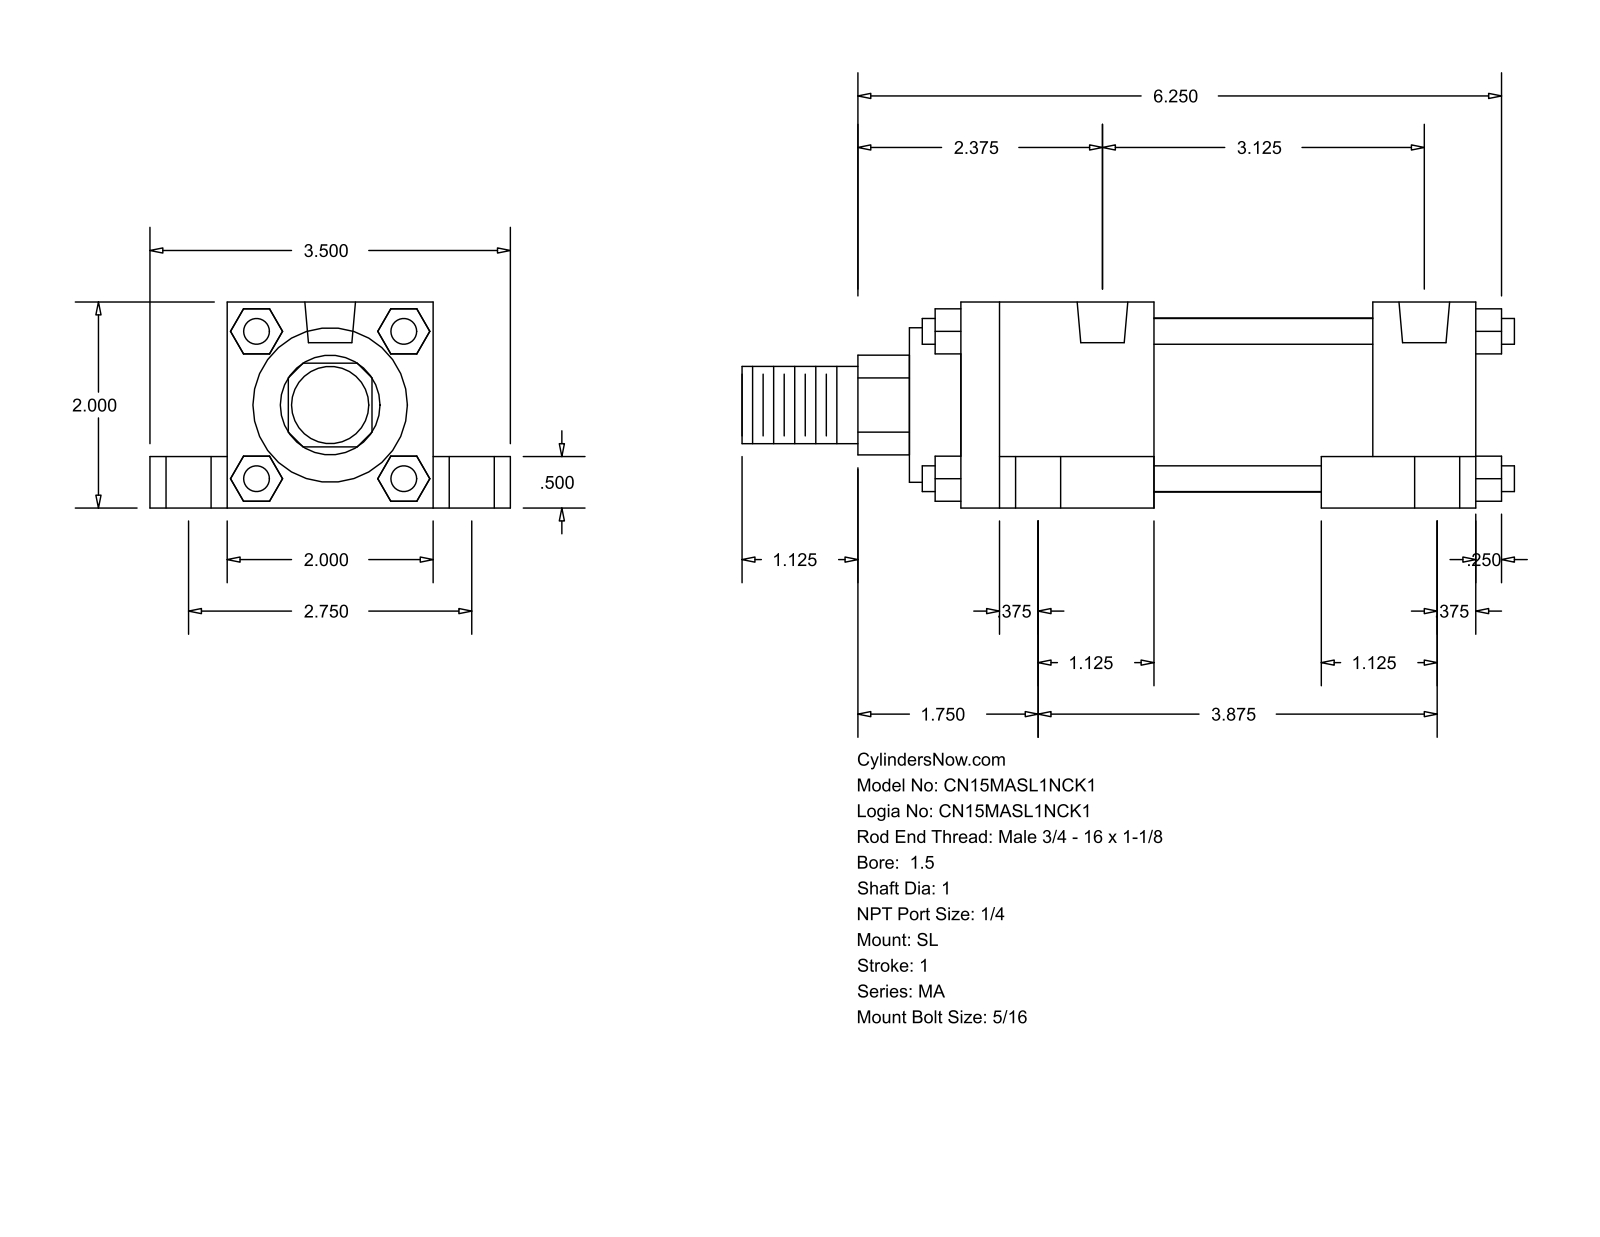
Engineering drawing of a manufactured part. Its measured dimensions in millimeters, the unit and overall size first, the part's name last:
Units: millimetres
Overall size (bounding box): 190.5 × 88.9 × 50.8
Round holes (diameter × count): ⌀7.94 ×4, ⌀11.11 ×4, ⌀17.46 ×4, ⌀12.49 ×2
Round bosses / shafts (diameter × count): ⌀6.35 ×4, ⌀42.93 ×1, ⌀38.1 ×1, ⌀25.4 ×1, ⌀19.05 ×1
Partial cylindrical surfaces — rounded edges, fillets, slot ends (radius × count): R12.29 ×1
Main face-to-face distances: 50.8, 12.7, 19.05, 69.85, 38.1, 101.6, 53.97, 9.52, 127, 25.4
Hole centre spacings: 35.06, 38.36, 69.84, 79.37, 89.63, 98.43, 101.45, 120.69
Bodies: 0 solids, 148 faces (112 planar, 36 cylindrical, 0 other)
Part name (STEP PRODUCT): MA_SL__0150_1
STEP written by: GSSL Pune (CONFIG_CONTROL_DESIGN)
